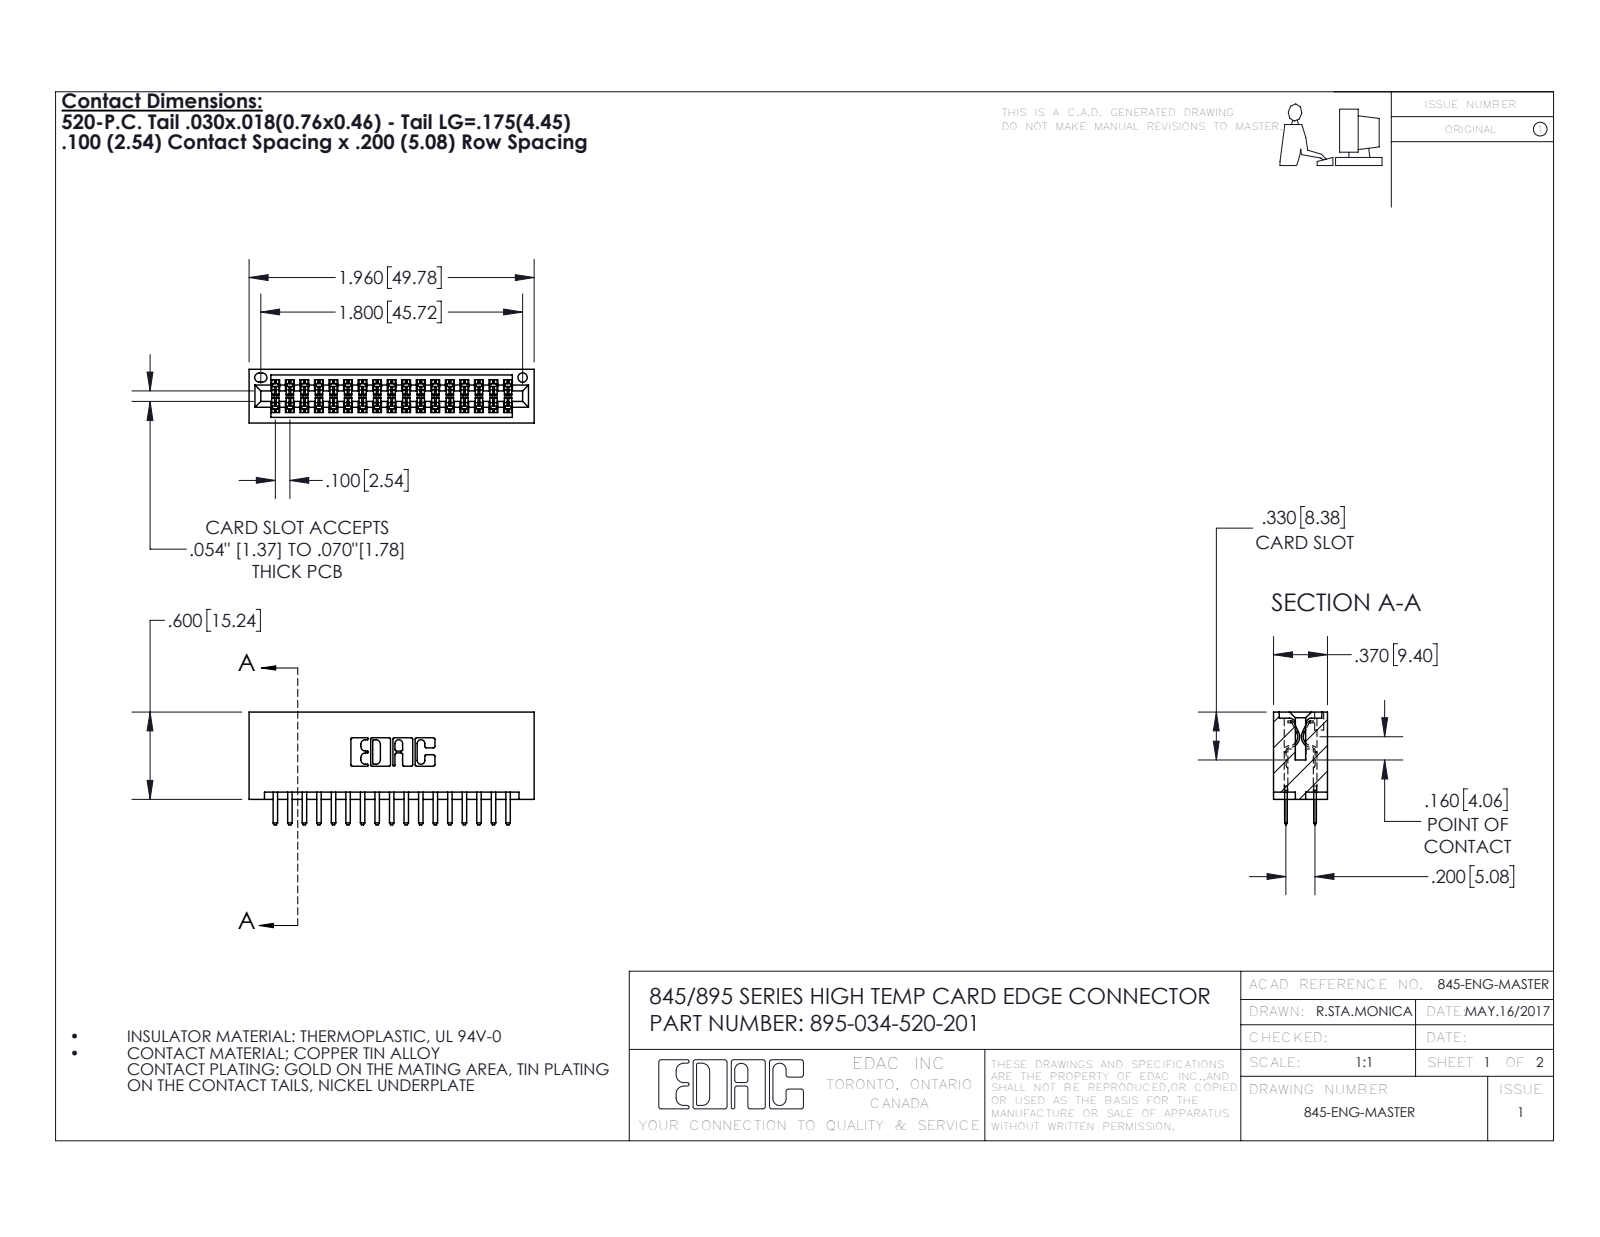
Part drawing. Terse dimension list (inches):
name: 345 Part_No Mounting Lugs; 345-292-001_345-293-120; 395-034-520-201
written by: SolidWorks 2016 (CONFIG_CONTROL_DESIGN)
unit: in
bodies: 35 solids, 1954 faces (1266 planar, 688 cylindrical, 0 other)
size: 1.96 × 0.775 × 0.37
volume: 0.318 in³; area: 11.6 in²
holes: 1× ⌀0.064
rounds: 51× R0.006, 38× R0.01, 22× R0.01, 6× R0.007, 6× R0.031, 3× R0.026, 2× R0.014, 2× R0.019
face distances: 0.2, 0.298, 0.072, 0.37, 0.098, 0.272, 0.025, 0.225, 0.1, 0.022
